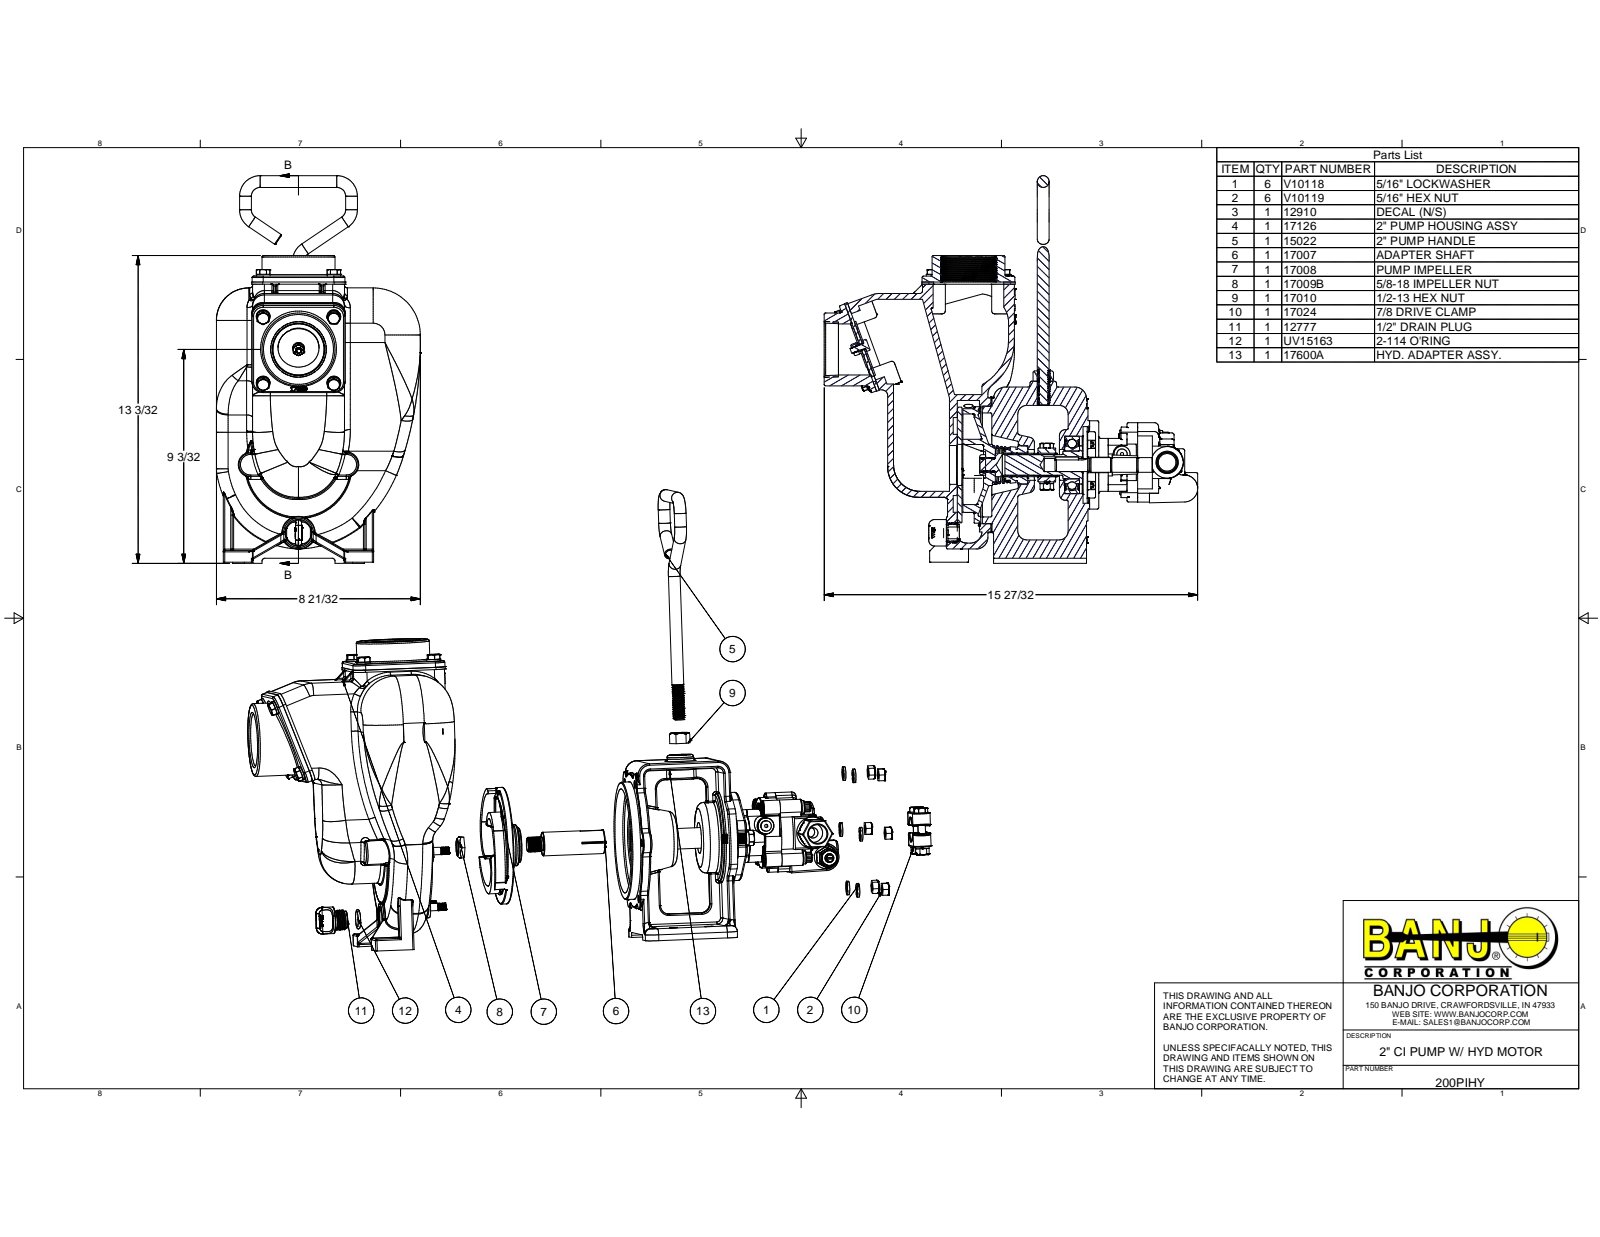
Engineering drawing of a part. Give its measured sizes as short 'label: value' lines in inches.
name: 200PIHY; 17126; 17026; 17000 (+8 more)
written by: Autodesk Inventor 2013 (AUTOMOTIVE_DESIGN)
unit: in
bodies: 92 solids, 6927 faces (1603 planar, 2310 cylindrical, 3014 other)
size: 16.479 × 15.854 × 8.658
volume: 195.5 in³; area: 1 531 in²
holes: 17× ⌀0.252, 16× ⌀0.322, 8× ⌀0.252, 8× ⌀0.313, 8× ⌀0.343, 6× ⌀0.38, 4× ⌀0.34, 3× ⌀0.187, 2× ⌀0.196, 2× ⌀0.25, 2× ⌀0.307, 2× ⌀0.35
bosses: 162× ⌀0.268, 34× ⌀0.324, 16× ⌀0.583, 12× ⌀0.313, 12× ⌀0.212, 8× ⌀0.312, 6× ⌀0.246, 5× ⌀0.5
rounds: 110× R0.03, 105× R0.062, 78× R0.06, 65× R0.25, 31× R0.125, 31× R0.5, 20× R0.063, 20× R0.438
face distances: 0.25, 0.281, 0.125, 3.65, 0.28, 1.464, 0.063, 1.815, 0.351, 0.337
hole spacings: 3, 2.121, 2.122, 2.813, 4.243, 2.121, 4.242, 4.243
